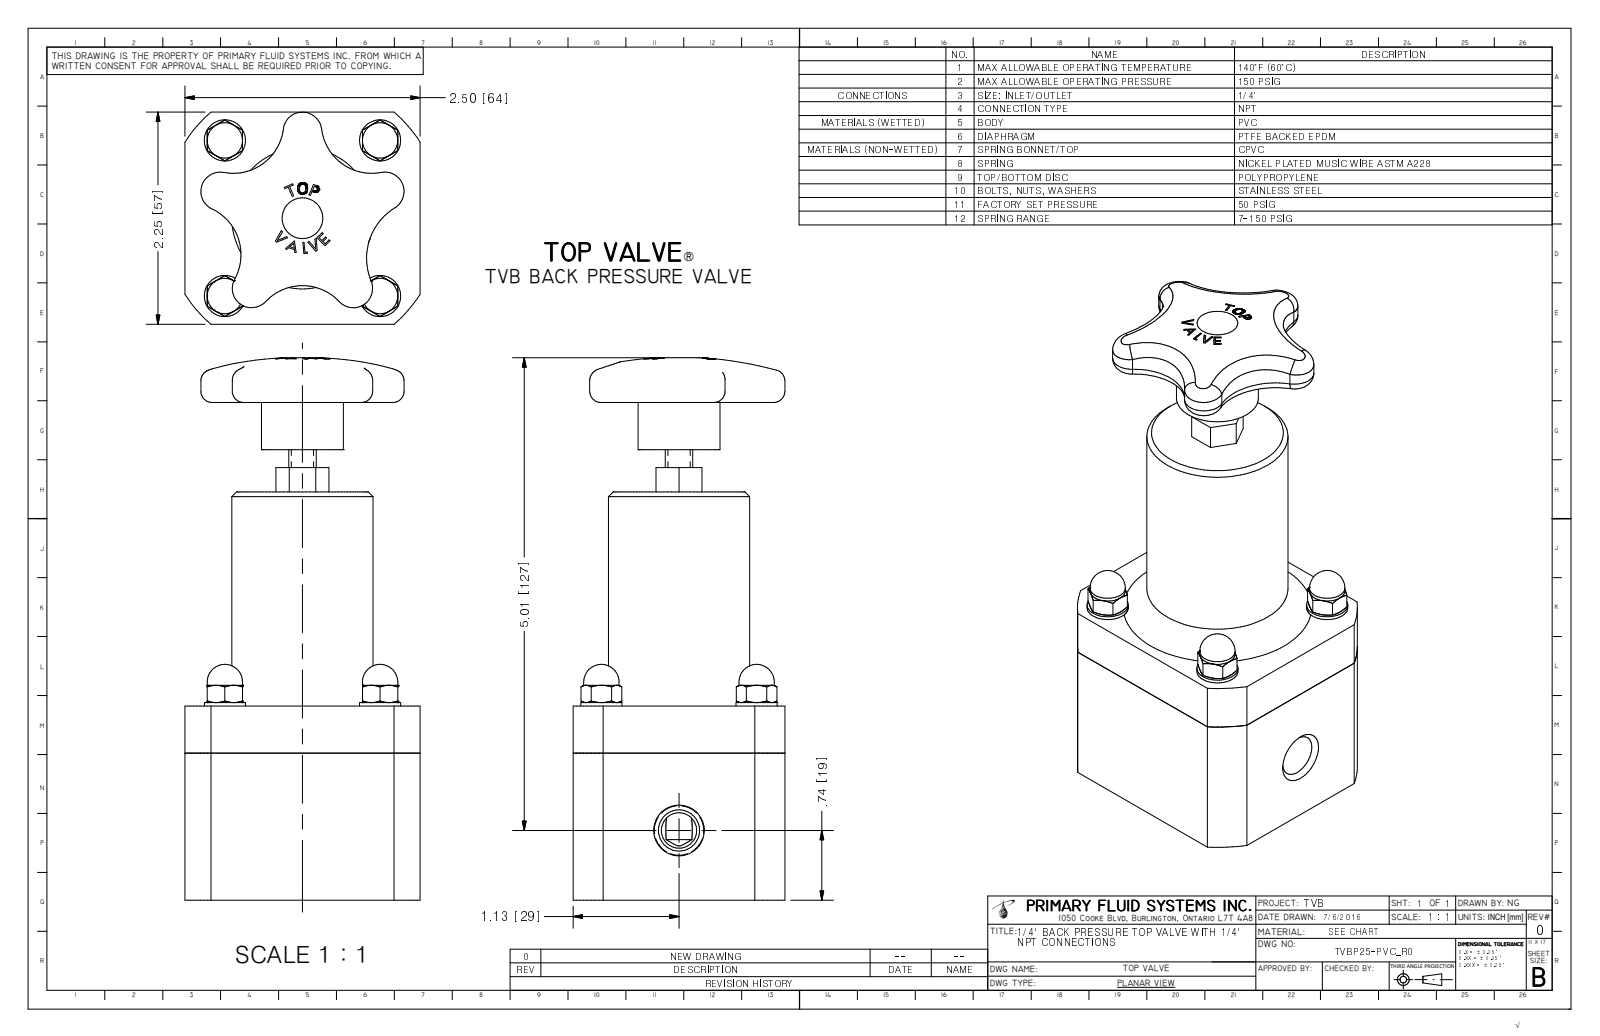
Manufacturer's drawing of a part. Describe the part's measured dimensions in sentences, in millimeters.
The part is named "TVBP25-PVC_R0". Its 3-D file was written by "Autodesk Inventor 2009 (AUTOMOTIVE_DESIGN)". It is 1 solid with 337 faces: 140 planar, 45 cylindrical and 152 other. Overall it measures 146.1 by 63.5 by 57.2 millimeters. Its volume is 270 100 cubic millimeters and its surface area 35 610 square millimeters. Round holes: 4 of diameter 3.7, 1 of diameter 11.1. Round bosses or shafts: 4 of diameter 11.1, 4 of diameter 9.5, 4 of diameter 7.9, 1 of diameter 38.1, 1 of diameter 22.1, 1 of diameter 7.4. Partial cylindrical surfaces (rounded edges, fillets, slot ends): 5 of radius 2.2, 5 of radius 5.2, 4 of radius 13.6, 4 of radius 16.7, 1 of radius 15.9, 1 of radius 18.9, 1 of radius 37.8. The main face-to-face distances are 57.2, 63.5, 52.3, 110, 57.7, 121.4, 69, 11.4, 15.2, 48.3. The hole center spacings are 41.9, 41.9, 59.3.
